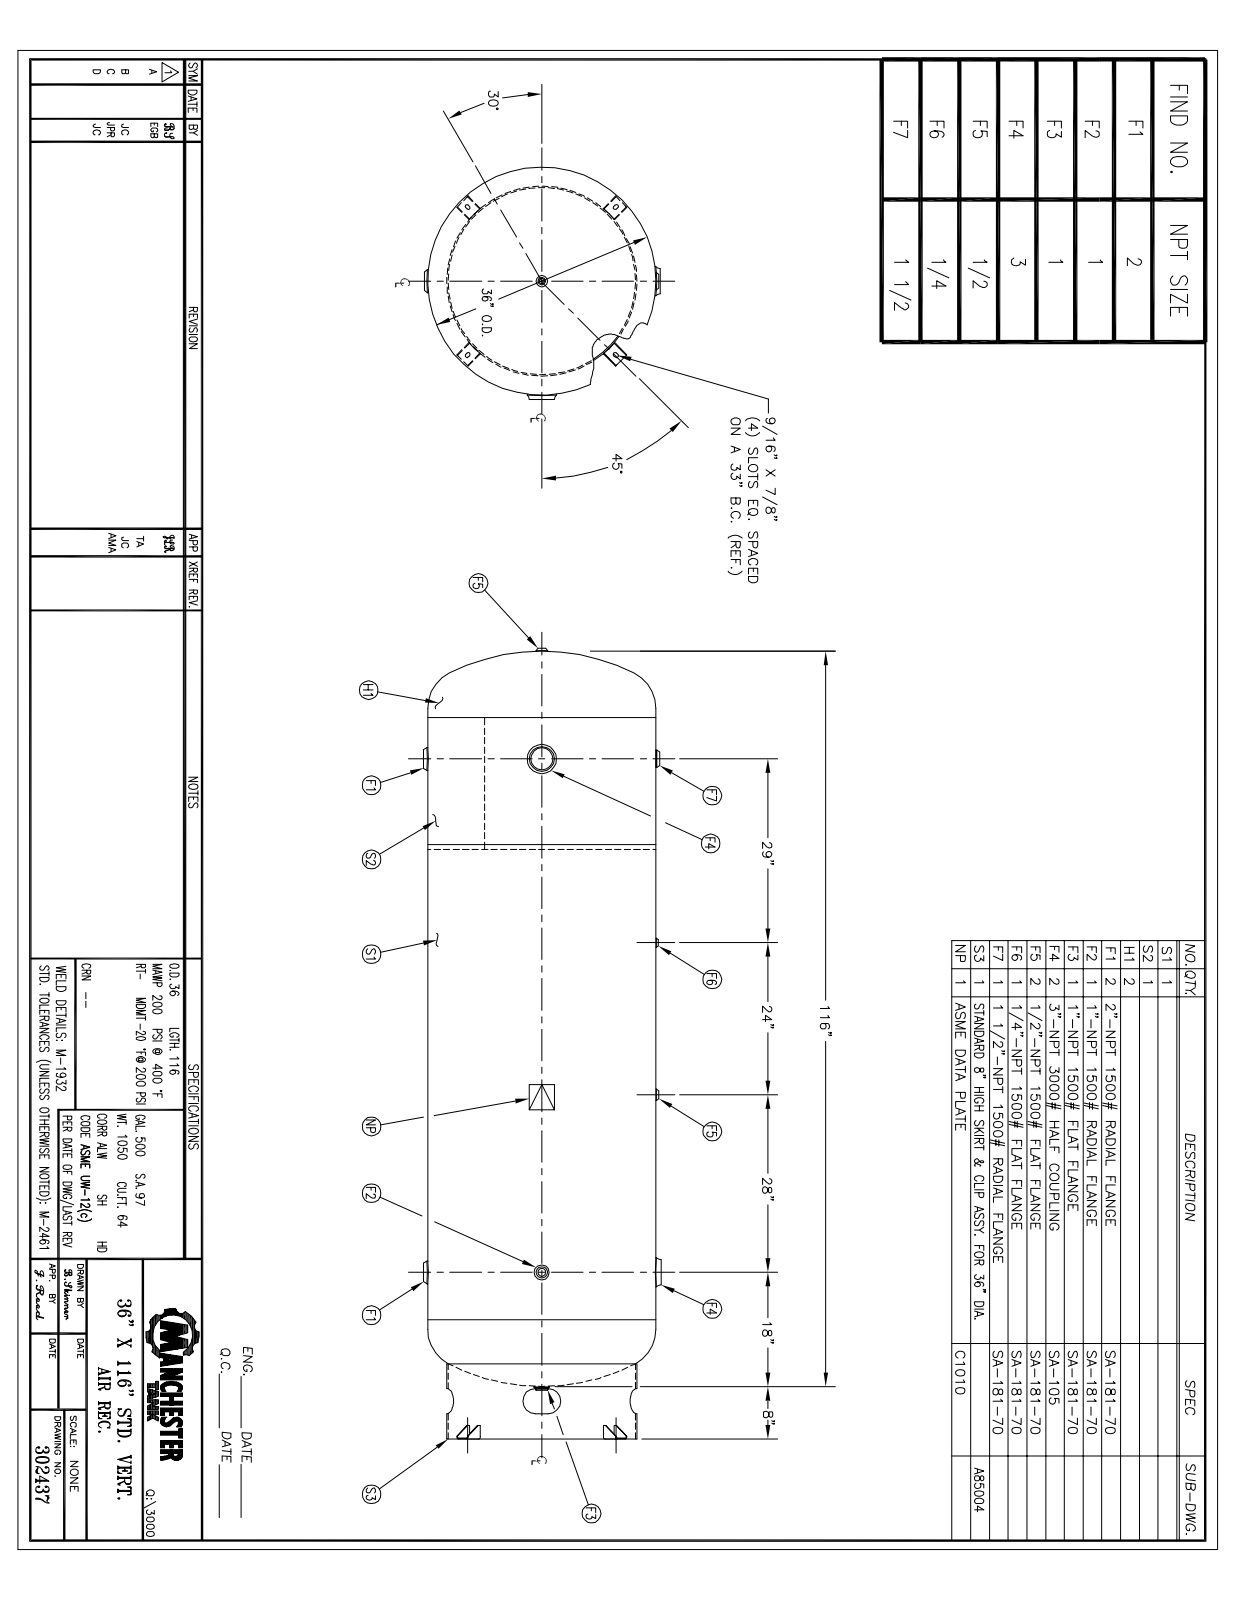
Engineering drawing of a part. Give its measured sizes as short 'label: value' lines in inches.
name: 302437
written by: SolidWorks 2011 (CONFIG_CONTROL_DESIGN)
unit: in
bodies: 0 solids, 259 faces (91 planar, 92 cylindrical, 76 other)
size: 124.78 × 37.487 × 36.76
holes: 2× ⌀0.84, 2× ⌀3.5, 1× ⌀0.54, 1× ⌀1.315, 1× ⌀1.315, 1× ⌀1.9, 1× ⌀2.375, 1× ⌀2.375, 1× ⌀29.546, 1× ⌀35.658
bosses: 2× ⌀4.25, 2× ⌀3.625, 2× ⌀2.375, 2× ⌀1.813, 1× ⌀36, 1× ⌀35.62, 1× ⌀30, 1× ⌀2.688
rounds: 8× R0.25, 8× R0.384, 7× R0.281, 1× R18.06
face distances: 0.134, 0.063, 2.446, 11.875, 101.936, 113.811, 23.75, 78.186, 90.061, 95
hole spacings: 81, 24, 28, 29, 52, 53
